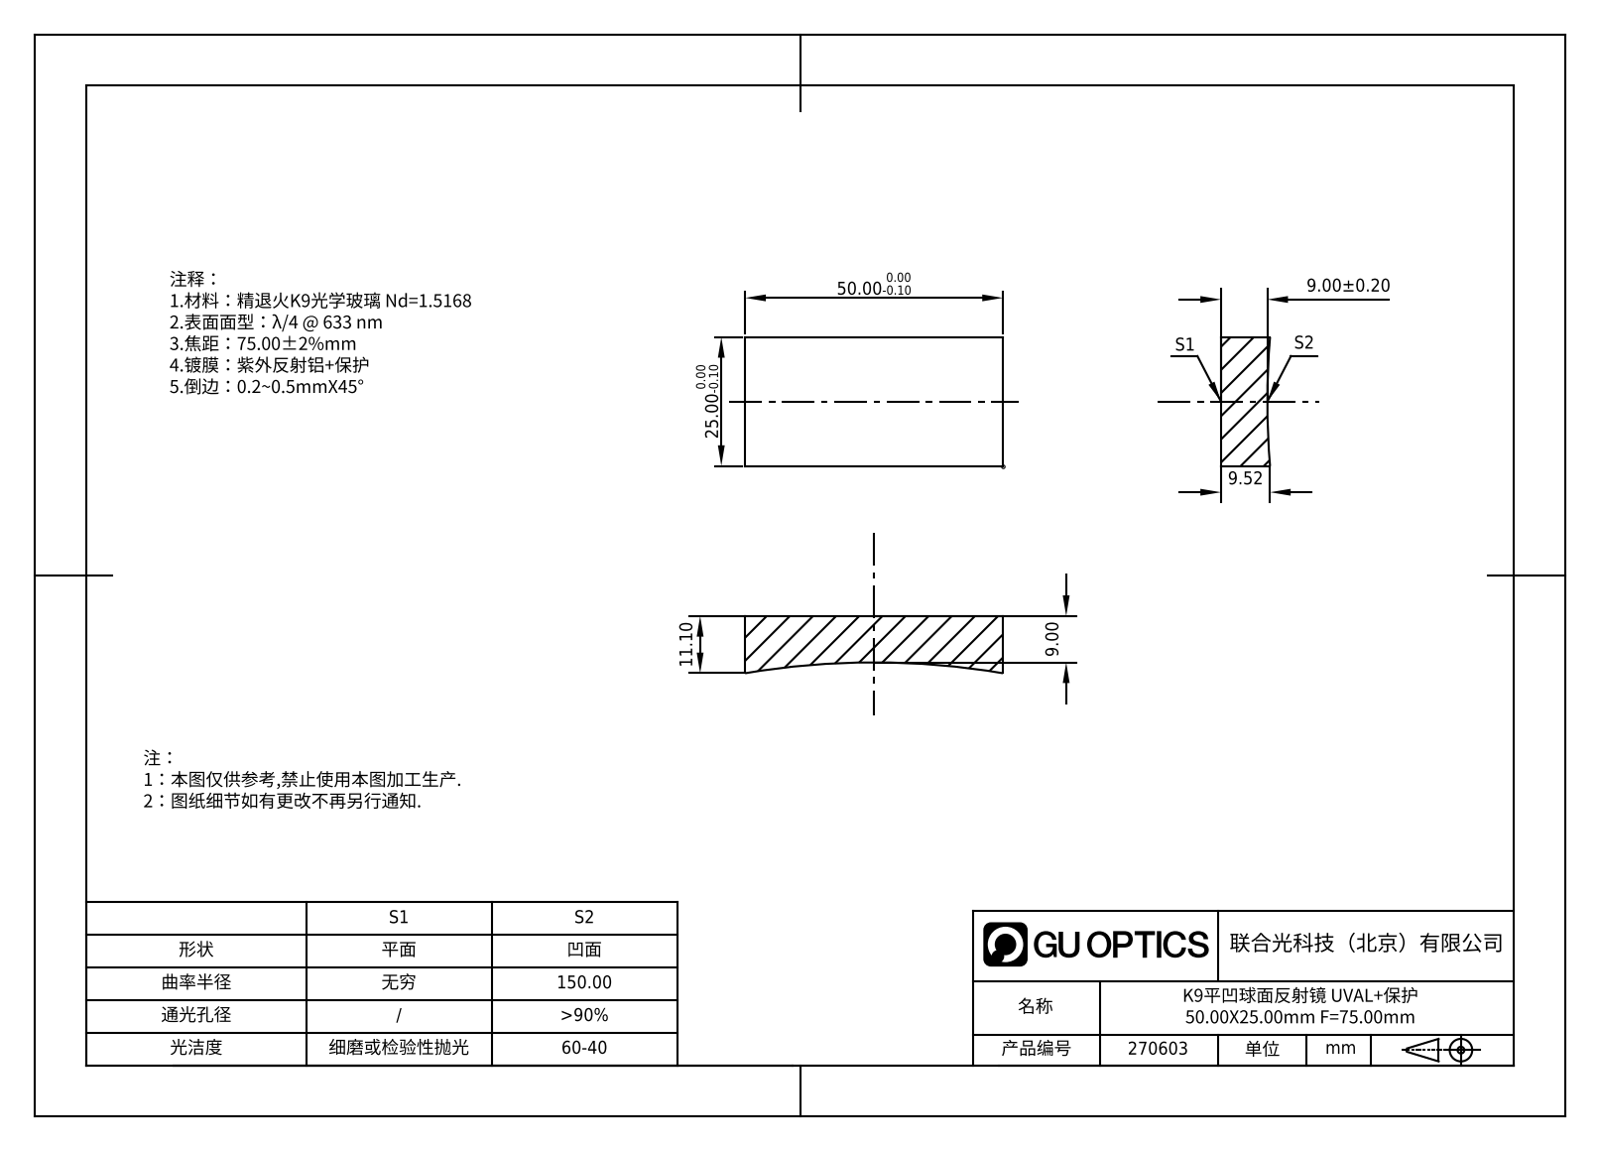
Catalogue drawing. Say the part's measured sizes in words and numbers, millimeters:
The part is named "GM13-50x25-075". Its 3-D file was written by "SolidWorks 2022 (AUTOMOTIVE_DESIGN)". It is 1 solid with 7 faces: 5 planar, 0 cylindrical and 2 other. Overall it measures 50 by 25 by 11.63 millimeters. Its volume is 12 340 cubic millimeters and its surface area 4 093 square millimeters. The main face-to-face distances are 25, 50.
